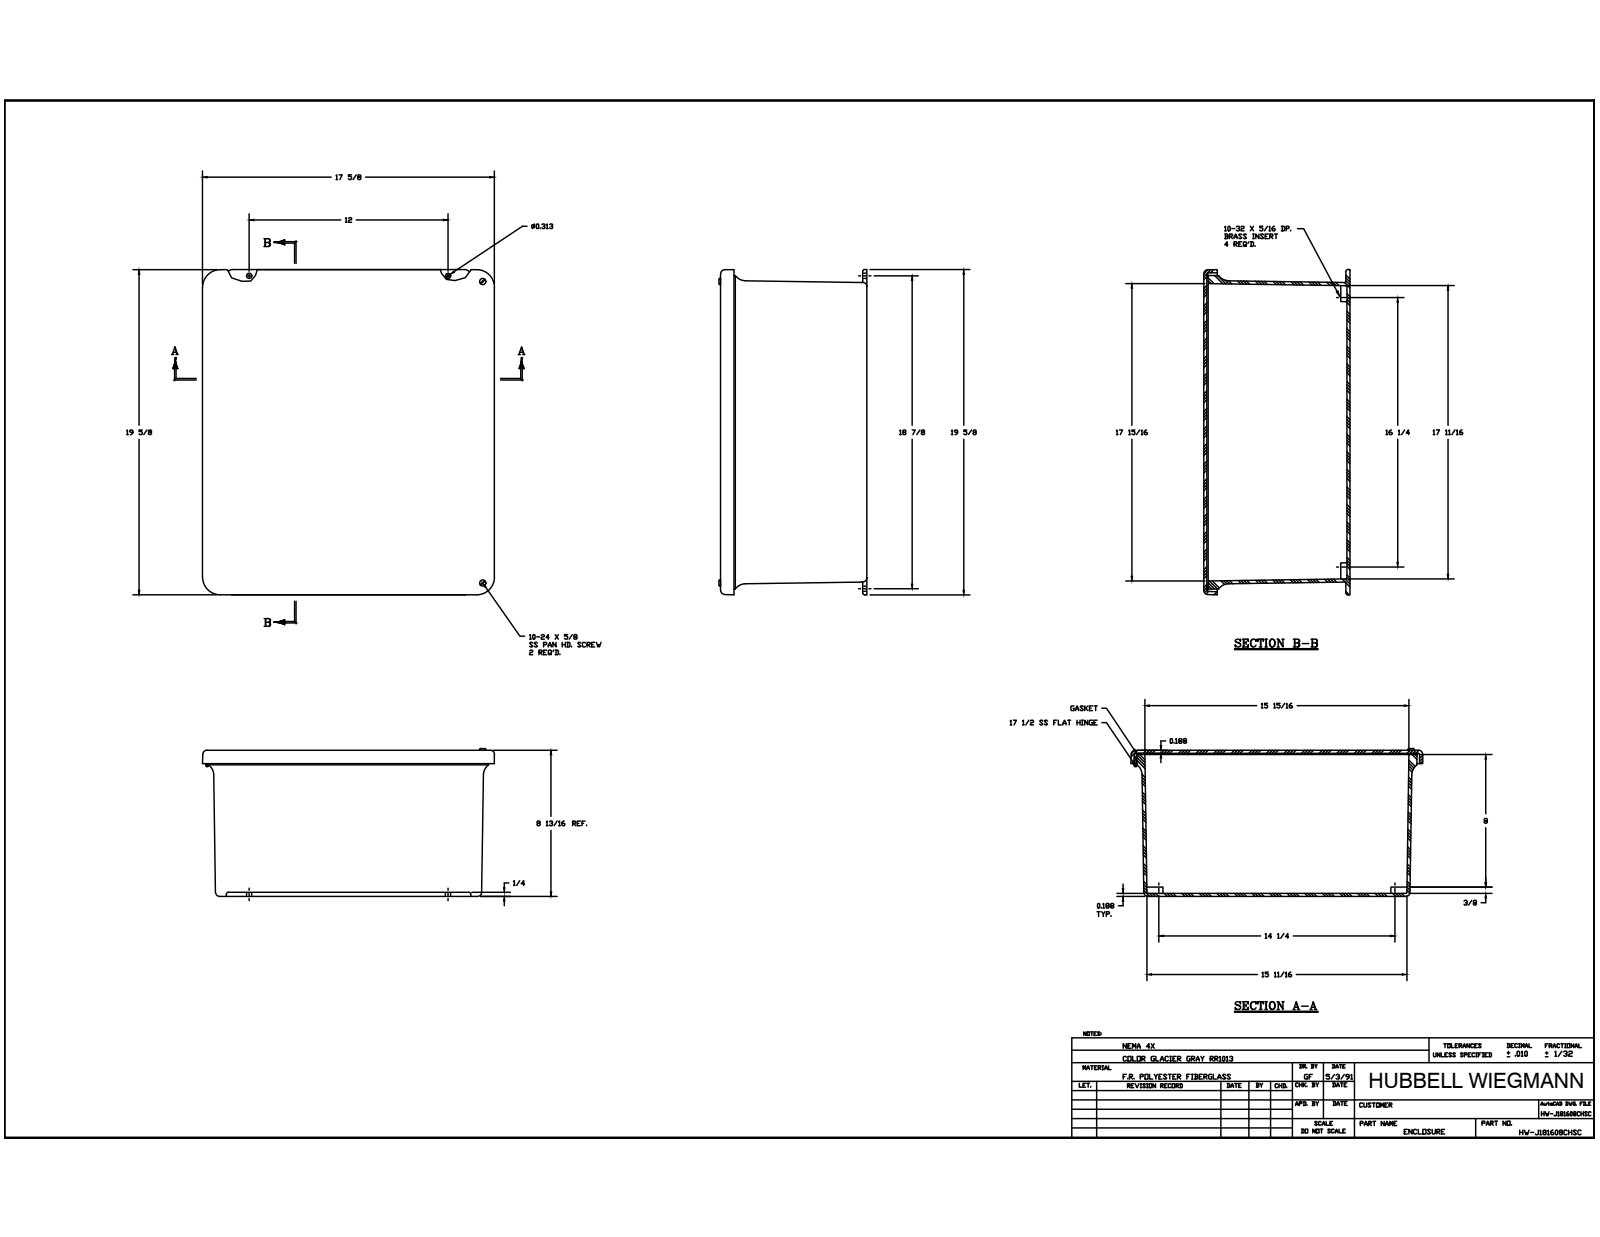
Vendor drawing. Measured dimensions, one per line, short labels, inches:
name: J1816HW_1; RMINS45821P_69; RMINS45821P_70; RMINS45821P_71 (+8 more)
written by: Autodesk Inventor 2014 (AUTOMOTIVE_DESIGN)
unit: in
bodies: 26 solids, 953 faces (369 planar, 371 cylindrical, 213 other)
size: 19.625 × 17.642 × 8.957
volume: 259.6 in³; area: 2 699 in²
holes: 12× ⌀0.131, 12× ⌀0.14, 5× ⌀0.152, 4× ⌀0.156, 4× ⌀0.218, 2× ⌀0.145, 1× ⌀0.085, 1× ⌀0.085
bosses: 12× ⌀0.25, 12× ⌀0.125, 6× ⌀0.27, 2× ⌀0.19, 2× ⌀0.156, 1× ⌀0.155
rounds: 20× R0.031, 12× R0.125, 8× R0.25, 6× R0.2, 4× R0.375, 4× R0.75, 2× R0.063
face distances: 0.187, 8.638, 8.826, 0.188, 8.45, 8.638, 0.302, 0.49, 8.563, 8.375
hole spacings: 3.375, 3.375, 6.75, 10.25, 0.25, 9.75, 10, 1.37
